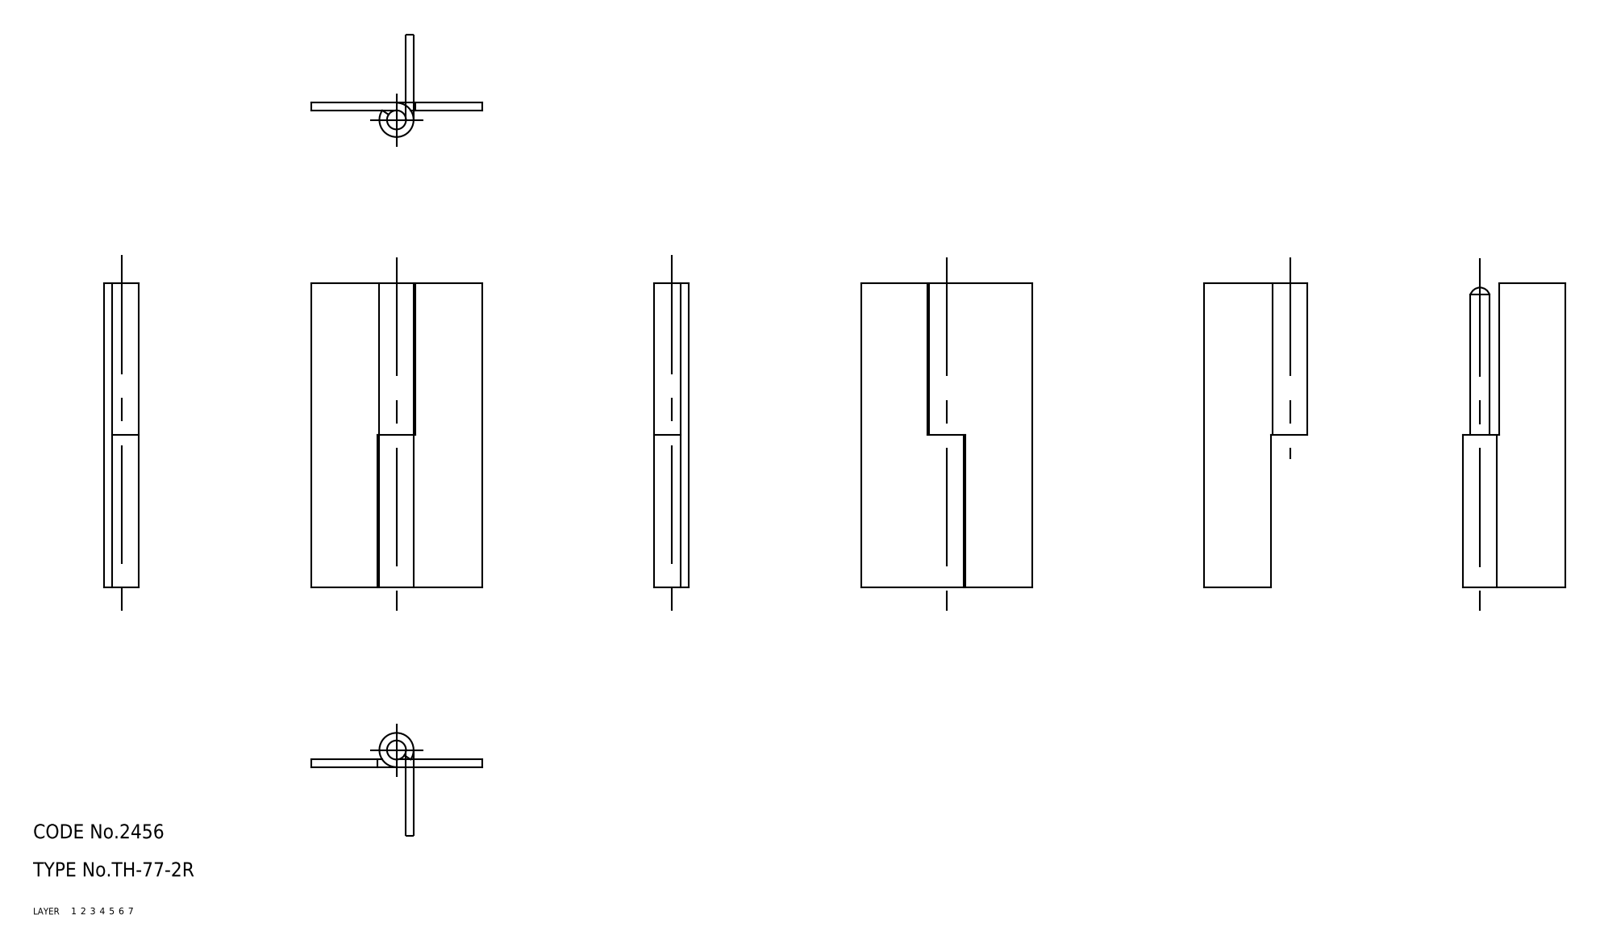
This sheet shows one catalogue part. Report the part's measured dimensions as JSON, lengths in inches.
{"part_name": "shaft; hinge piece_B; hinge piece_A; TH_77_2R_16044_36", "step_written_by": "CADfix (AUTOMOTIVE_DESIGN)", "units": "inches", "bodies": {"solids": 3, "faces": 24, "planar": 0, "cylindrical": 0, "other": 24}, "overall_size": [2.52, 1.417, 0.283], "volume_in3": 0.34, "surface_area_in2": 11.49}
